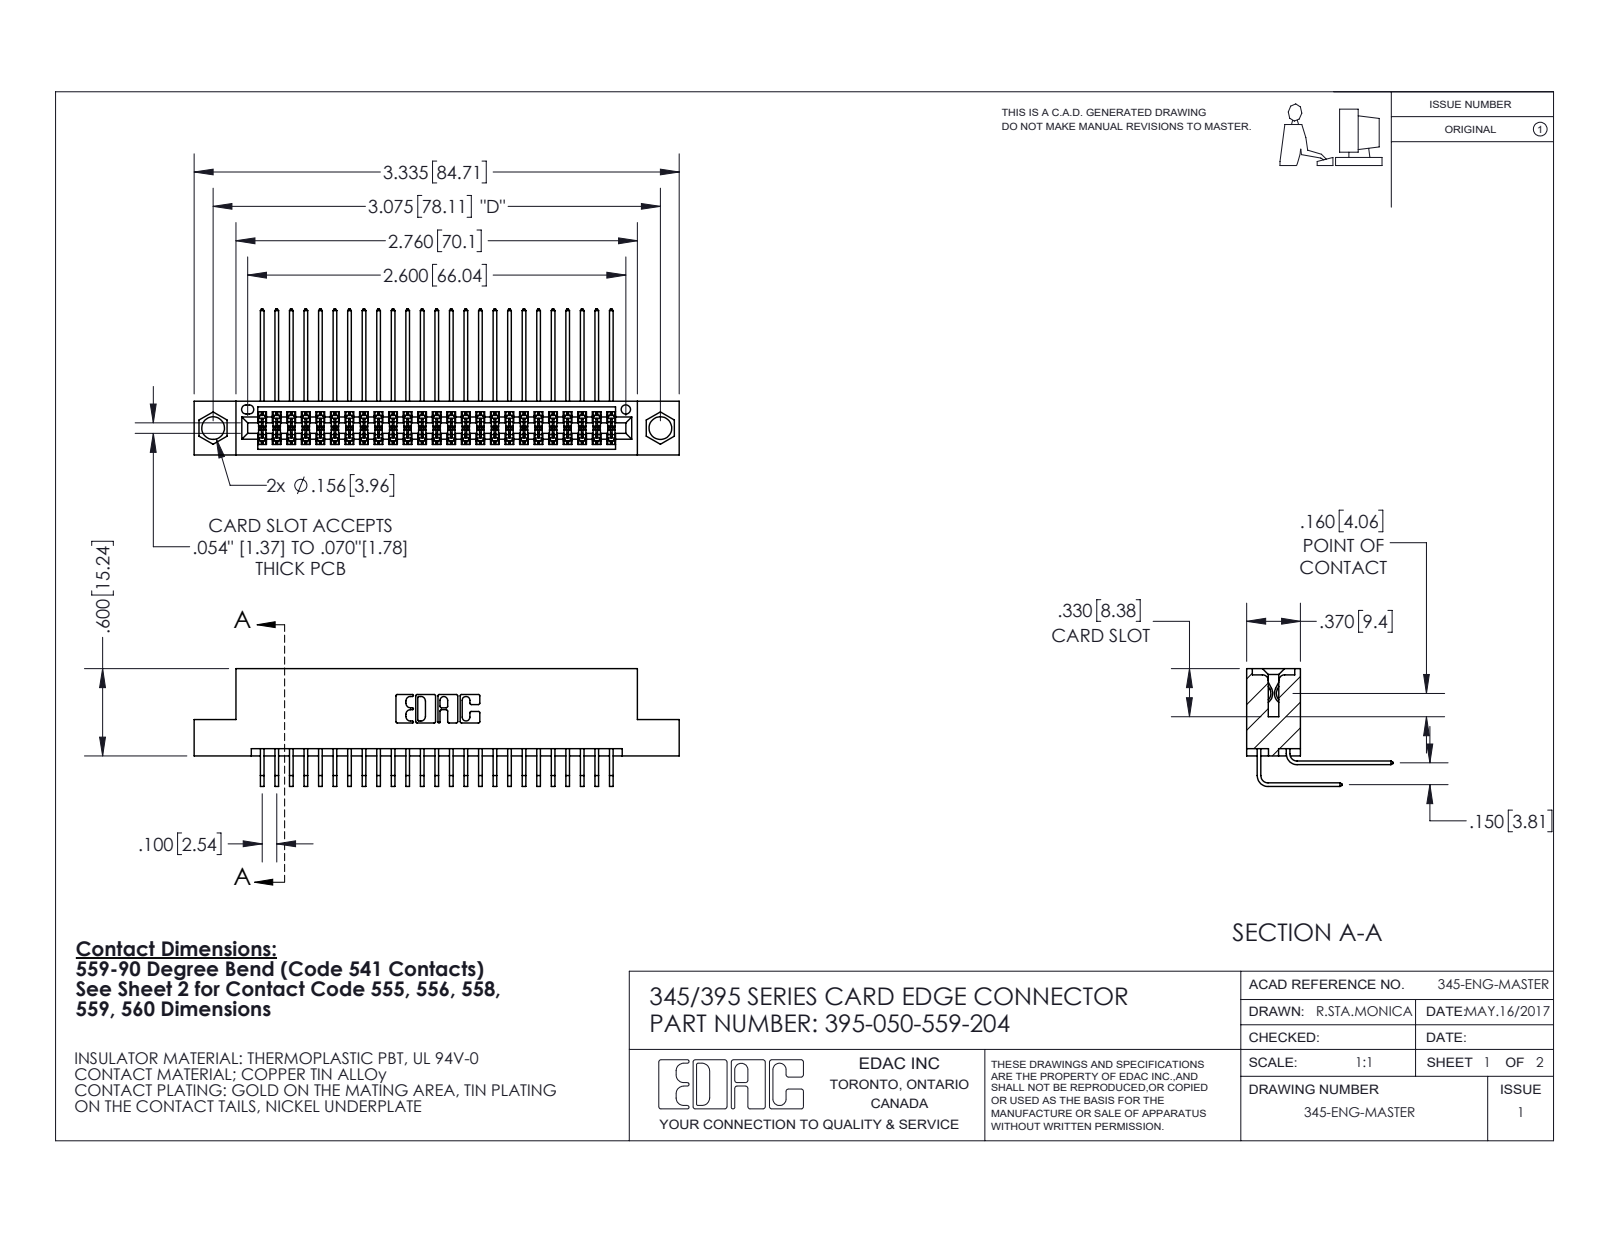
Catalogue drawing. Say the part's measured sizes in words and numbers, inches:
The part is named "345-292-001_559 Tail - 2; 345-292-001_558 559 Tail - 1; 395-050-559-204; 345 Part_Flush Mounting Lugs - 0.156 Dia-TI". Its 3-D file was written by "SolidWorks 2020 (CONFIG_CONTROL_DESIGN)". It is 51 solids with 2740 faces: 1844 planar, 896 cylindrical and 0 other. Overall it measures 3.335 by 1.005 by 0.809 inches. Its volume is 0.504 cubic inches and its surface area 20.27 square inches. Round holes: 2 of diameter 0.156, 1 of diameter 0.064. Partial cylindrical surfaces (rounded edges, fillets, slot ends): 100 of radius 0.006, 22 of radius 0.01, 6 of radius 0.007, 6 of radius 0.031, 3 of radius 0.026, 2 of radius 0.014, 2 of radius 0.019, 2 of radius 0.022. The main face-to-face distances are 0.072, 0.298, 0.2, 0.37, 0.098, 0.272, 0.025, 0.225, 0.15, 0.175. The hole center spacings are 0.27, 2.84, 3.075.
